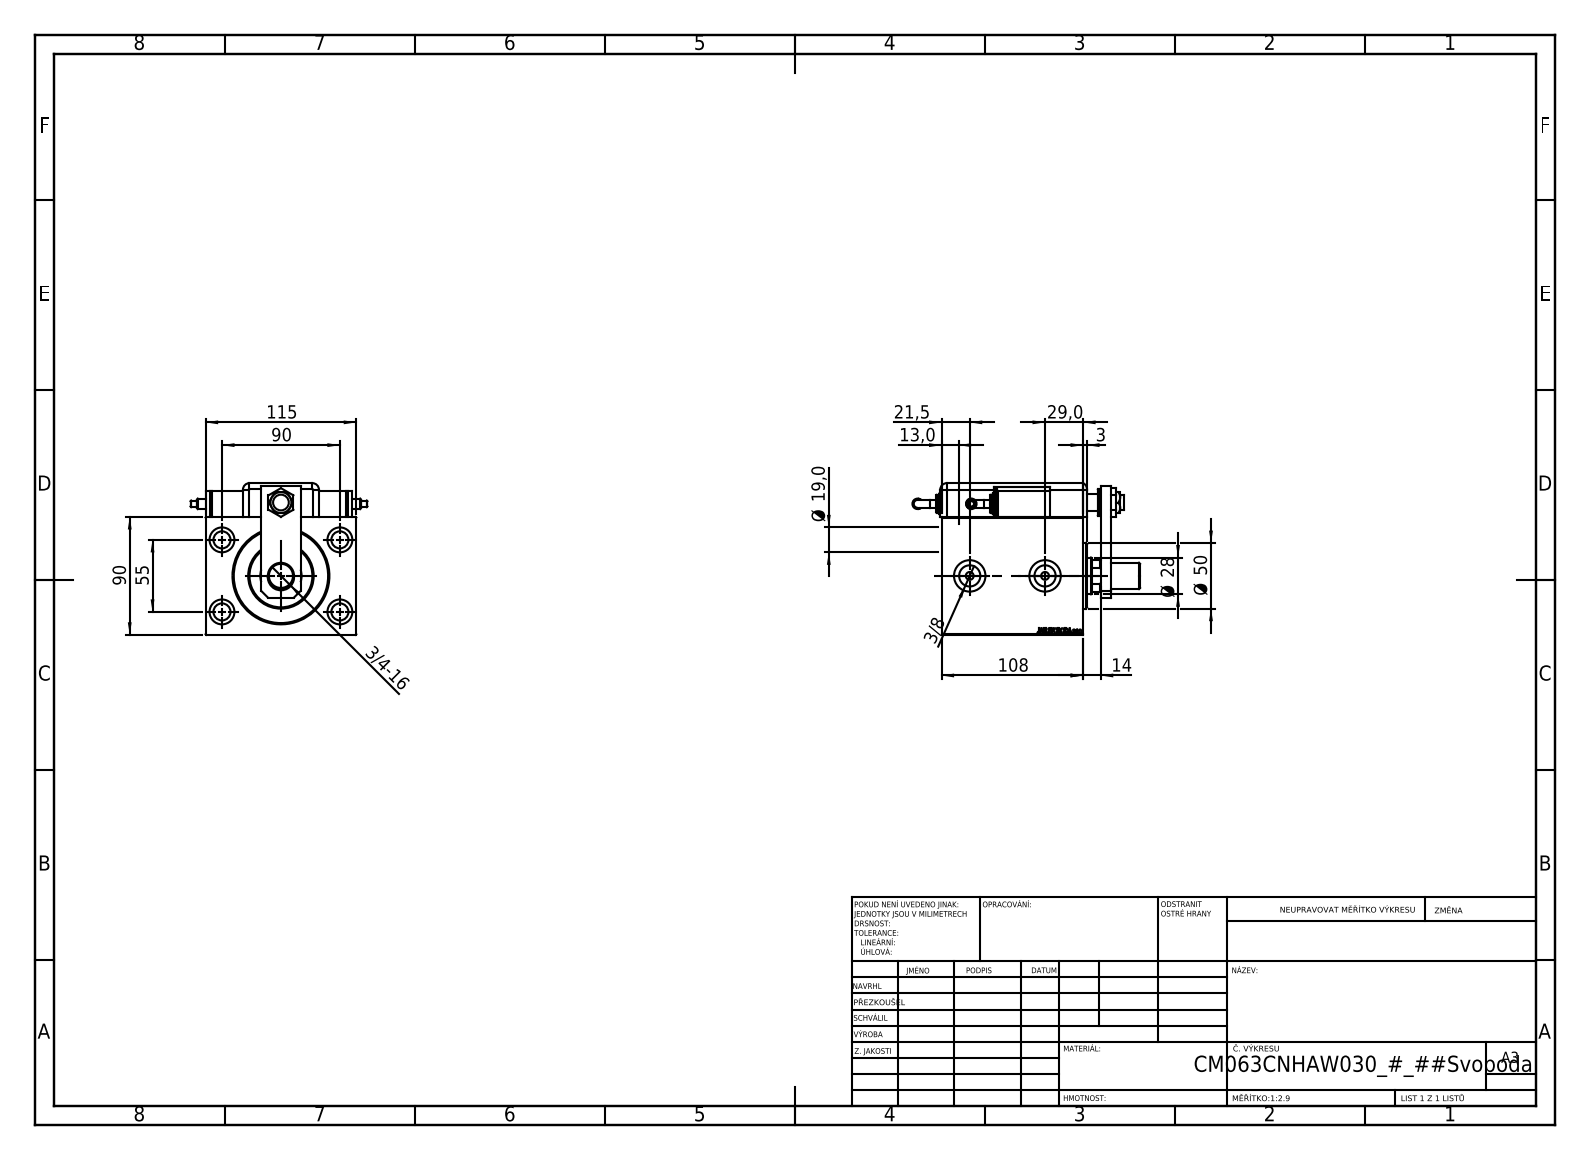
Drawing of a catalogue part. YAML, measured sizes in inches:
part_name: "V450CM_C_VCP; TYC; V450CM_MALE_METRIC; MAGNETIC SWITCH Q (+8 more)"
step_written_by: "SolidWorks 2019 (CONFIG_CONTROL_DESIGN)"
units: inches
bodies: {solids: 14, faces: 1291, planar: 623, cylindrical: 129, other: 539}
overall_size: [6.841, 5.315, 4.559]
volume: 68.77
surface_area: 306.8
round_holes:
  - {diameter: 0.512, count: 5}
  - {diameter: 0.748, count: 4}
  - {diameter: 0.157, count: 2}
  - {diameter: 0.236, count: 2}
  - {diameter: 0.315, count: 2}
  - {diameter: 0.637, count: 2}
  - {diameter: 0.945, count: 2}
  - {diameter: 0.472, count: 1}
  - {diameter: 0.551, count: 1}
  - {diameter: 0.728, count: 1}
  - {diameter: 0.787, count: 1}
  - {diameter: 1.102, count: 1}
round_bosses_or_shafts:
  - {diameter: 0.787, count: 4}
  - {diameter: 0.63, count: 2}
  - {diameter: 0.551, count: 2}
  - {diameter: 0.315, count: 2}
  - {diameter: 0.236, count: 2}
  - {diameter: 0.198, count: 2}
  - {diameter: 1.969, count: 1}
  - {diameter: 0.709, count: 1}
partial_cylinders:
  - {radius: 0.197, count: 9}
  - {radius: 0.394, count: 1}
  - {radius: 0.531, count: 1}
face_to_face_distances: [3.543, 0.118, 4.252, 4.528, 3.563, 0.689, 0.531, 0.728, 0.315, 1.016]
hole_center_spacings: [2.076, 2.097, 2.056, 2.165, 3.543, 3.734, 4.153, 0.039]
